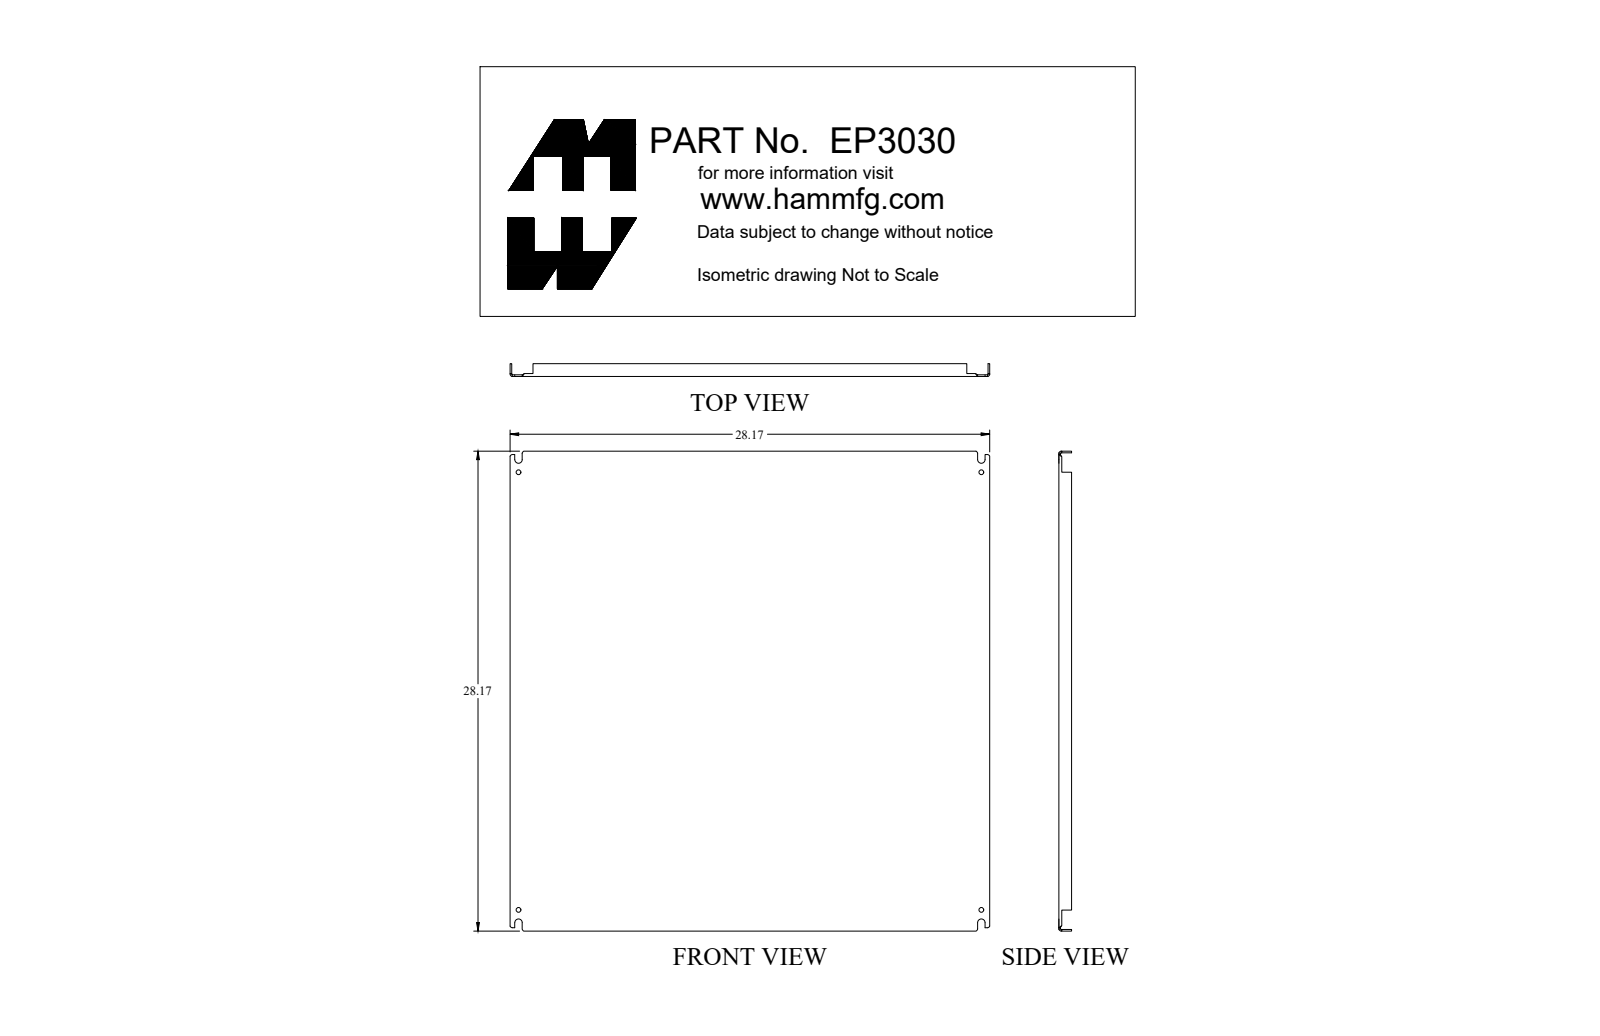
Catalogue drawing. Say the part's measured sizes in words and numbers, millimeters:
The part is named "EP3030". Its 3-D file was written by "SolidWorks 2018 (AUTOMOTIVE_DESIGN)". It is 1 solid with 128 faces: 74 planar, 38 cylindrical and 16 other. Overall it measures 715.5 by 715.5 by 19.1 millimeters. Its volume is 1 331 000 cubic millimeters and its surface area 1 110 000 square millimeters. Round holes: 4 of diameter 7.1. Partial cylindrical surfaces (rounded edges, fillets, slot ends): 4 of radius 1.2, 4 of radius 1.6, 4 of radius 3.6, 4 of radius 5.6. The main face-to-face distances are 2.4, 713.1, 710.7, 715.5, 19.1, 16.6, 4.3, 1.9, 14.7, 31.4. The hole center spacings are 652.5, 690.6, 950.1.
